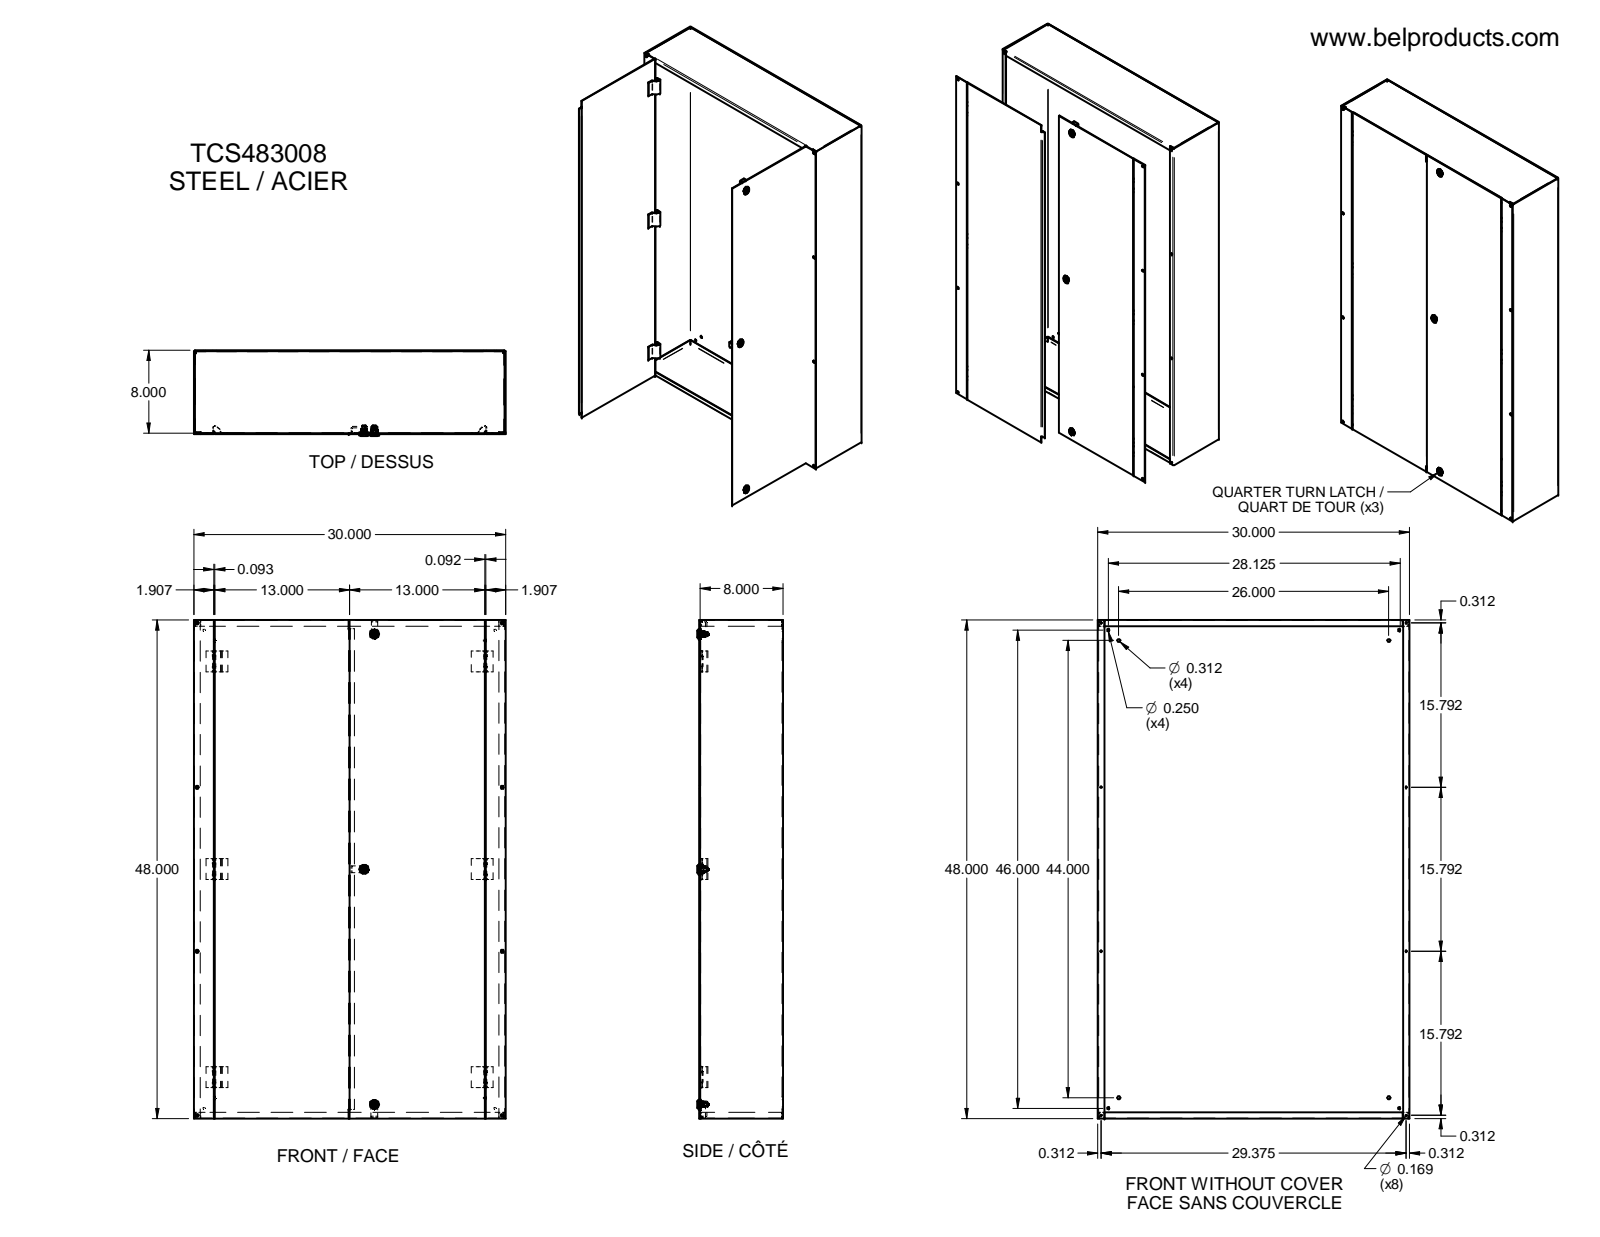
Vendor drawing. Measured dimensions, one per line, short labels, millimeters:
name: LOCK AVEC TOURNEVIS TYPE 4-12 SANS CAME; HOSING-oa0; INSERT POUR TOURNEVIS-oa1; NOIX DE FIXATION-oa2 (+8 more)
written by: Unknown (AUTOMOTIVE_DESIGN)
unit: mm
bodies: 46 solids, 1693 faces (850 planar, 421 cylindrical, 422 other)
size: 1219.2 × 762 × 209.57
volume: 5 288 000 mm³; area: 5 606 000 mm²
holes: 12× ⌀7.92, 8× ⌀4.29, 4× ⌀6.35, 3× ⌀9.1, 3× ⌀11.18, 3× ⌀12.83, 3× ⌀15.8, 3× ⌀17.46, 2× ⌀3.81, 2× ⌀6.99
bosses: 3× ⌀22.86, 3× ⌀22.61, 3× ⌀15.75, 3× ⌀12.95, 3× ⌀12.62, 3× ⌀12.19, 3× ⌀11.86, 3× ⌀10.08
rounds: 34× R9.53, 24× R0.25, 17× R0.81, 14× R2.72, 6× R9.42, 4× R1.52, 4× R3.05, 3× R3.48
face distances: 1.91, 203.2, 201.29, 1.9, 205.11, 760.1, 1217.3, 762, 758.2, 1219.2
hole spacings: 847.1, 24.69, 35.92, 60.61, 360.8, 384.05, 401.11, 686.27
